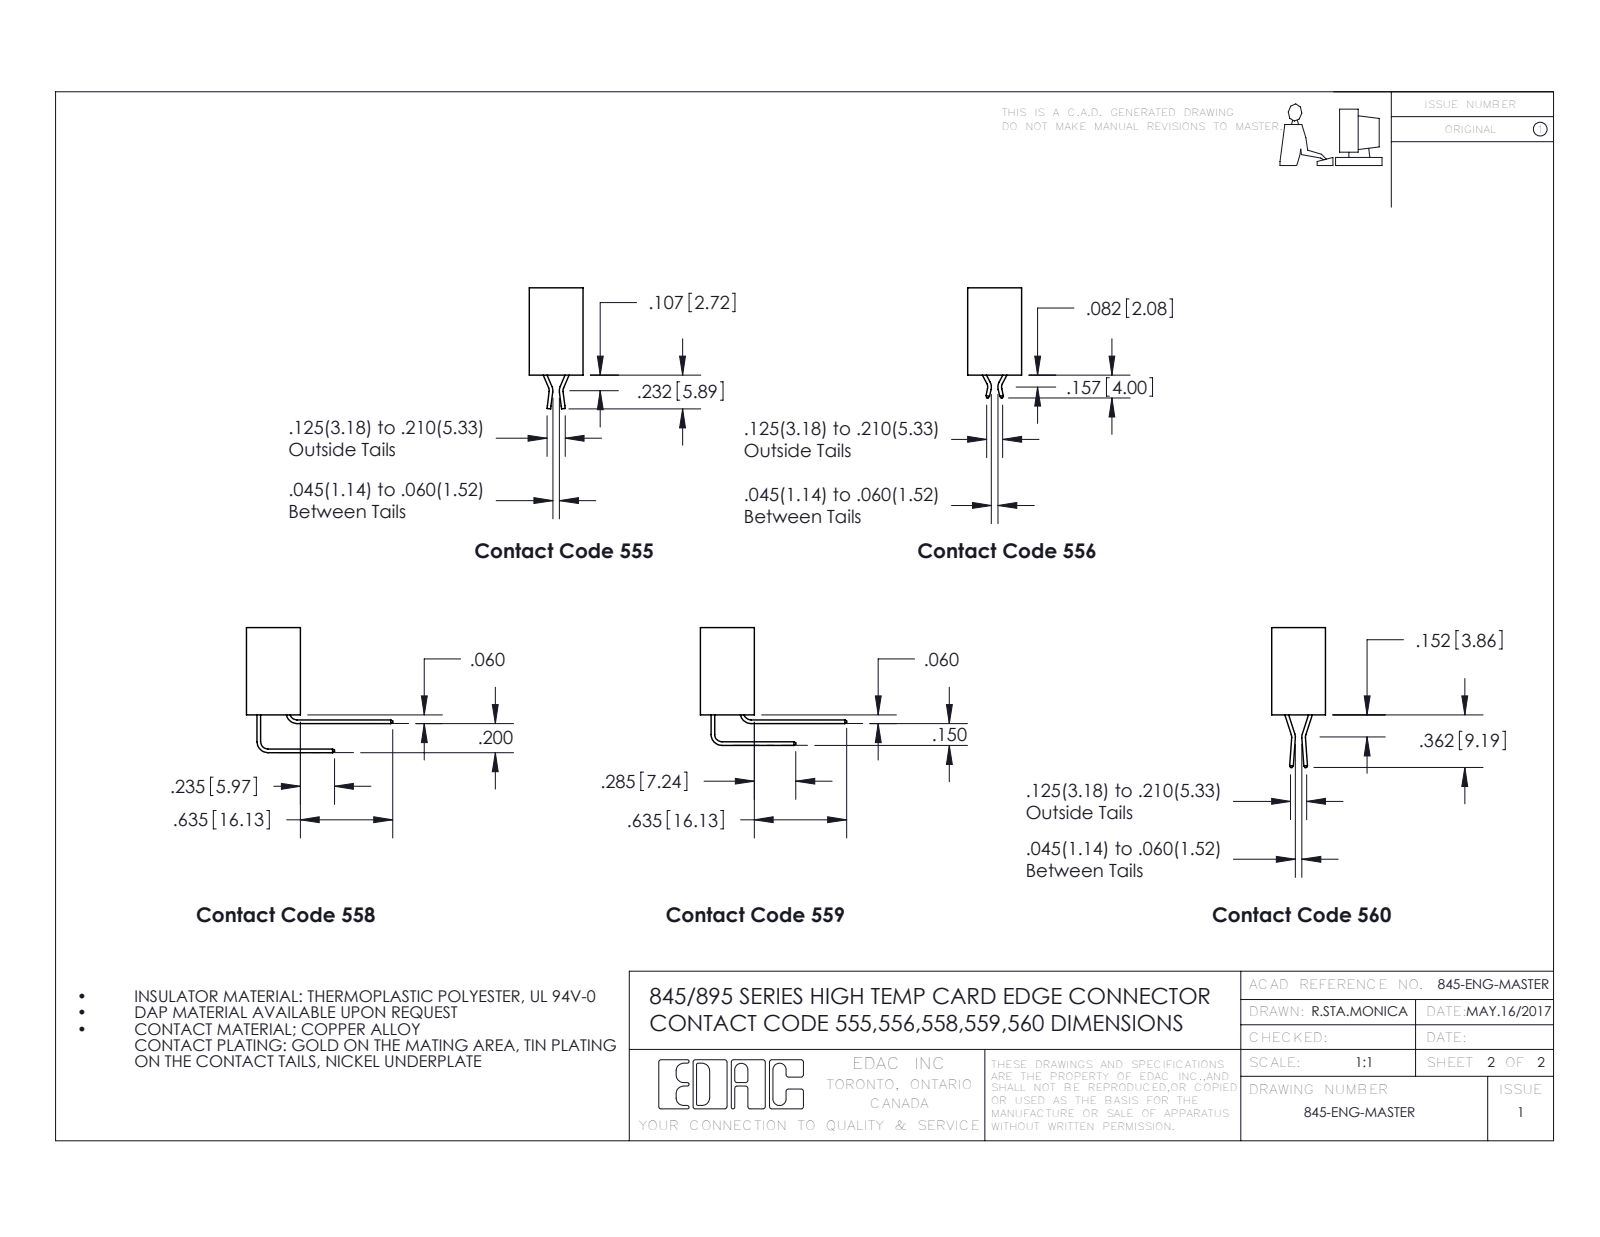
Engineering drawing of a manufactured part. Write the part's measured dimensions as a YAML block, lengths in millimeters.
part_name: "345-022-559-201; 345-292-001_559 Tail - 2; 345-292-001_558 559 Tail - 1; 345 Part_No Mounting Lugs"
step_written_by: "SolidWorks 2016 (CONFIG_CONTROL_DESIGN)"
units: millimeters
bodies: {solids: 23, faces: 1262, planar: 846, cylindrical: 416, other: 0}
overall_size: [34.5, 25.5, 20.5]
volume: 3820
surface_area: 5932
round_holes:
  - {diameter: 1.6, count: 1}
partial_cylinders:
  - {radius: 0.2, count: 33}
  - {radius: 0.3, count: 22}
  - {radius: 0.2, count: 6}
  - {radius: 0.8, count: 6}
  - {radius: 0.7, count: 3}
  - {radius: 0.4, count: 2}
  - {radius: 0.5, count: 2}
  - {radius: 0.6, count: 2}
face_to_face_distances: [5.1, 1.8, 7.6, 9.4, 2.5, 2.5, 6.9, 0.6, 15.2, 3.8]
